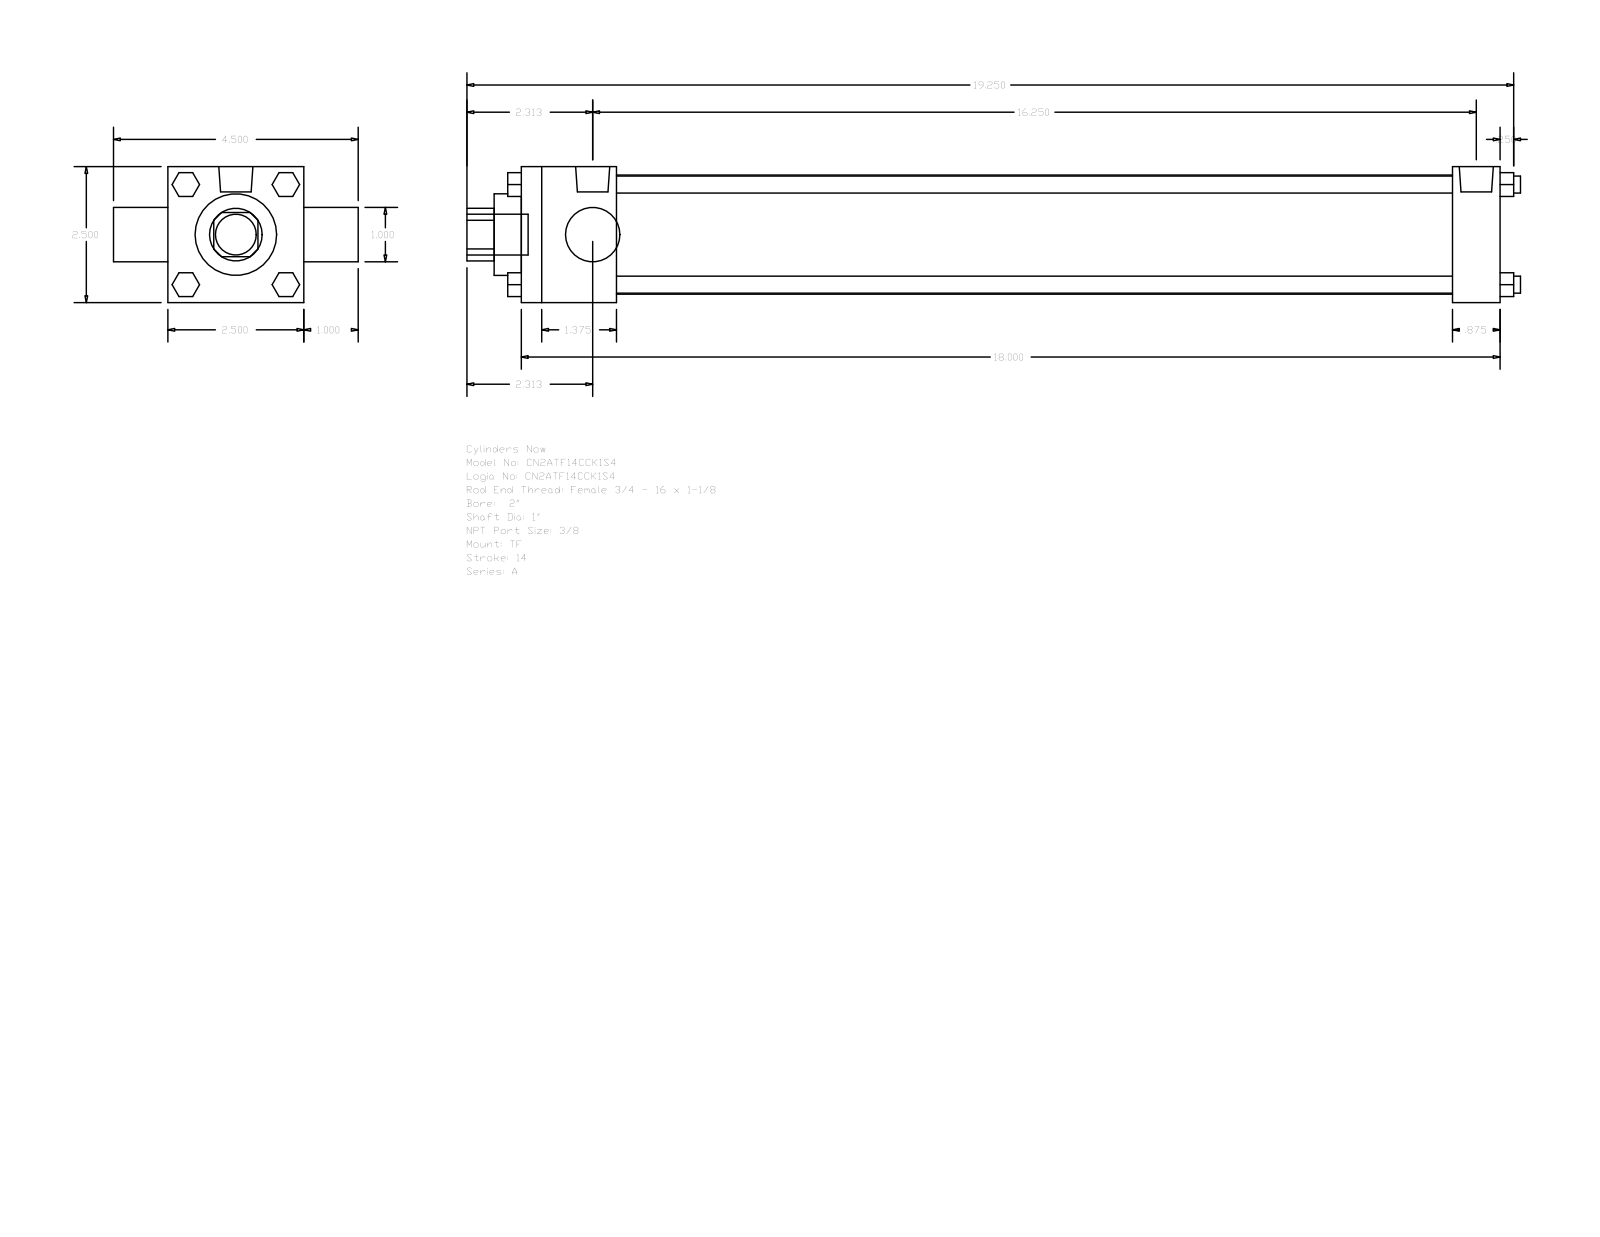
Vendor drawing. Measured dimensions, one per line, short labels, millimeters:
name: A_TF__0200_1
written by: GSSL Pune (CONFIG_CONTROL_DESIGN)
unit: mm
bodies: 0 solids, 120 faces (92 planar, 28 cylindrical, 0 other)
size: 492.12 × 114.3 × 63.5
holes: 2× ⌀25.4, 1× ⌀38.1, 1× ⌀55.63
bosses: 4× ⌀7.94, 3× ⌀5.56, 2× ⌀15.93, 1× ⌀19.05
rounds: 1× R12.29
face distances: 63.5, 457.2, 44.45, 434.98, 390.53, 412.75, 22.22, 25.4, 88.9, 469.9
